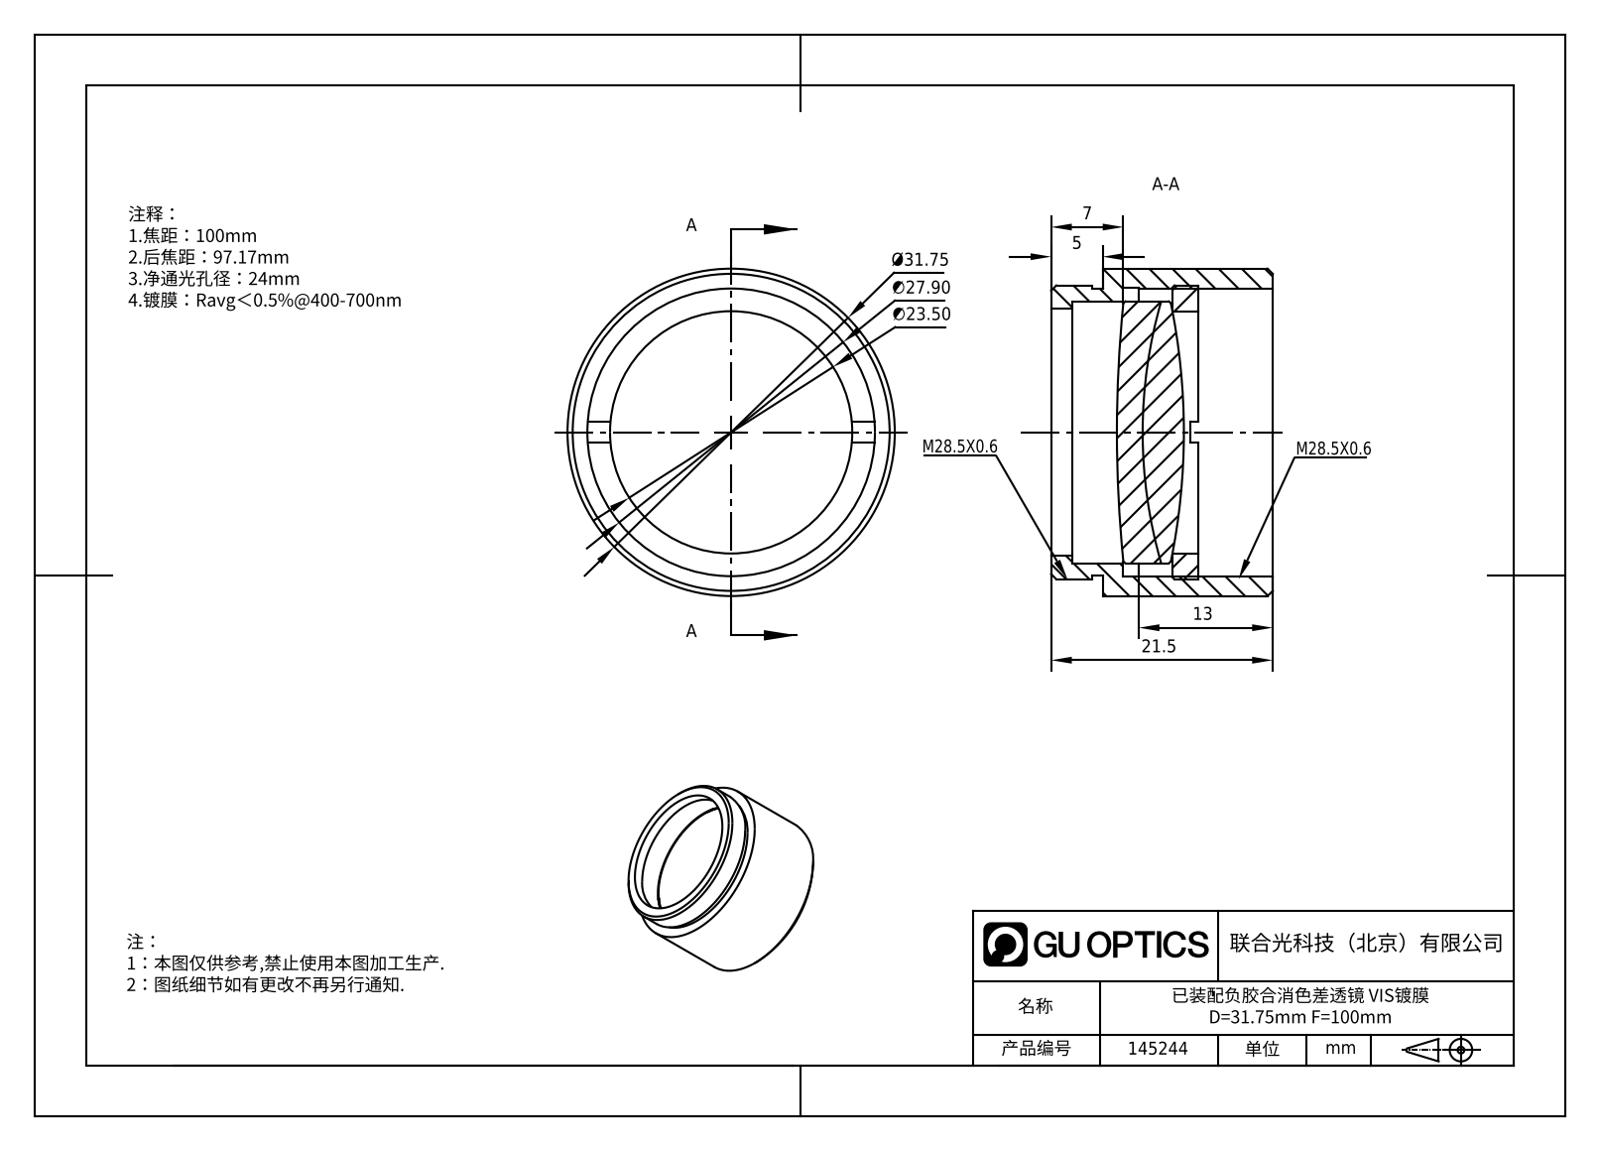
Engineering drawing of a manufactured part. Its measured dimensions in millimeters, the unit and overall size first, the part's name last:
Units: millimetres
Overall size (bounding box): 31.76 × 31.76 × 21.5
Round holes (diameter × count): ⌀23.5 ×1, ⌀24 ×1, ⌀27.9 ×1, ⌀28 ×1
Round bosses / shafts (diameter × count): ⌀31.76 ×1, ⌀28.5 ×1, ⌀27.8 ×1, ⌀25.4 ×1
Main face-to-face distances: 2, 5, 2.5, 6.76, 9.26, 11.76, 14.26, 21.5, 16.5, 9.74
Volume: 7 195 mm³ · Surface area: 7 819 mm²
Bodies: 4 solids, 56 faces (16 planar, 22 cylindrical, 18 other)
Part name (STEP PRODUCT): M28.5x0.6安装环PN35021-LM254-D2; M28.5x0.6ѹȦ; GL31-025B-100-VIS_Solidworks; APD-ML25-100-VIS
STEP written by: SolidWorks 2022 (AUTOMOTIVE_DESIGN)
